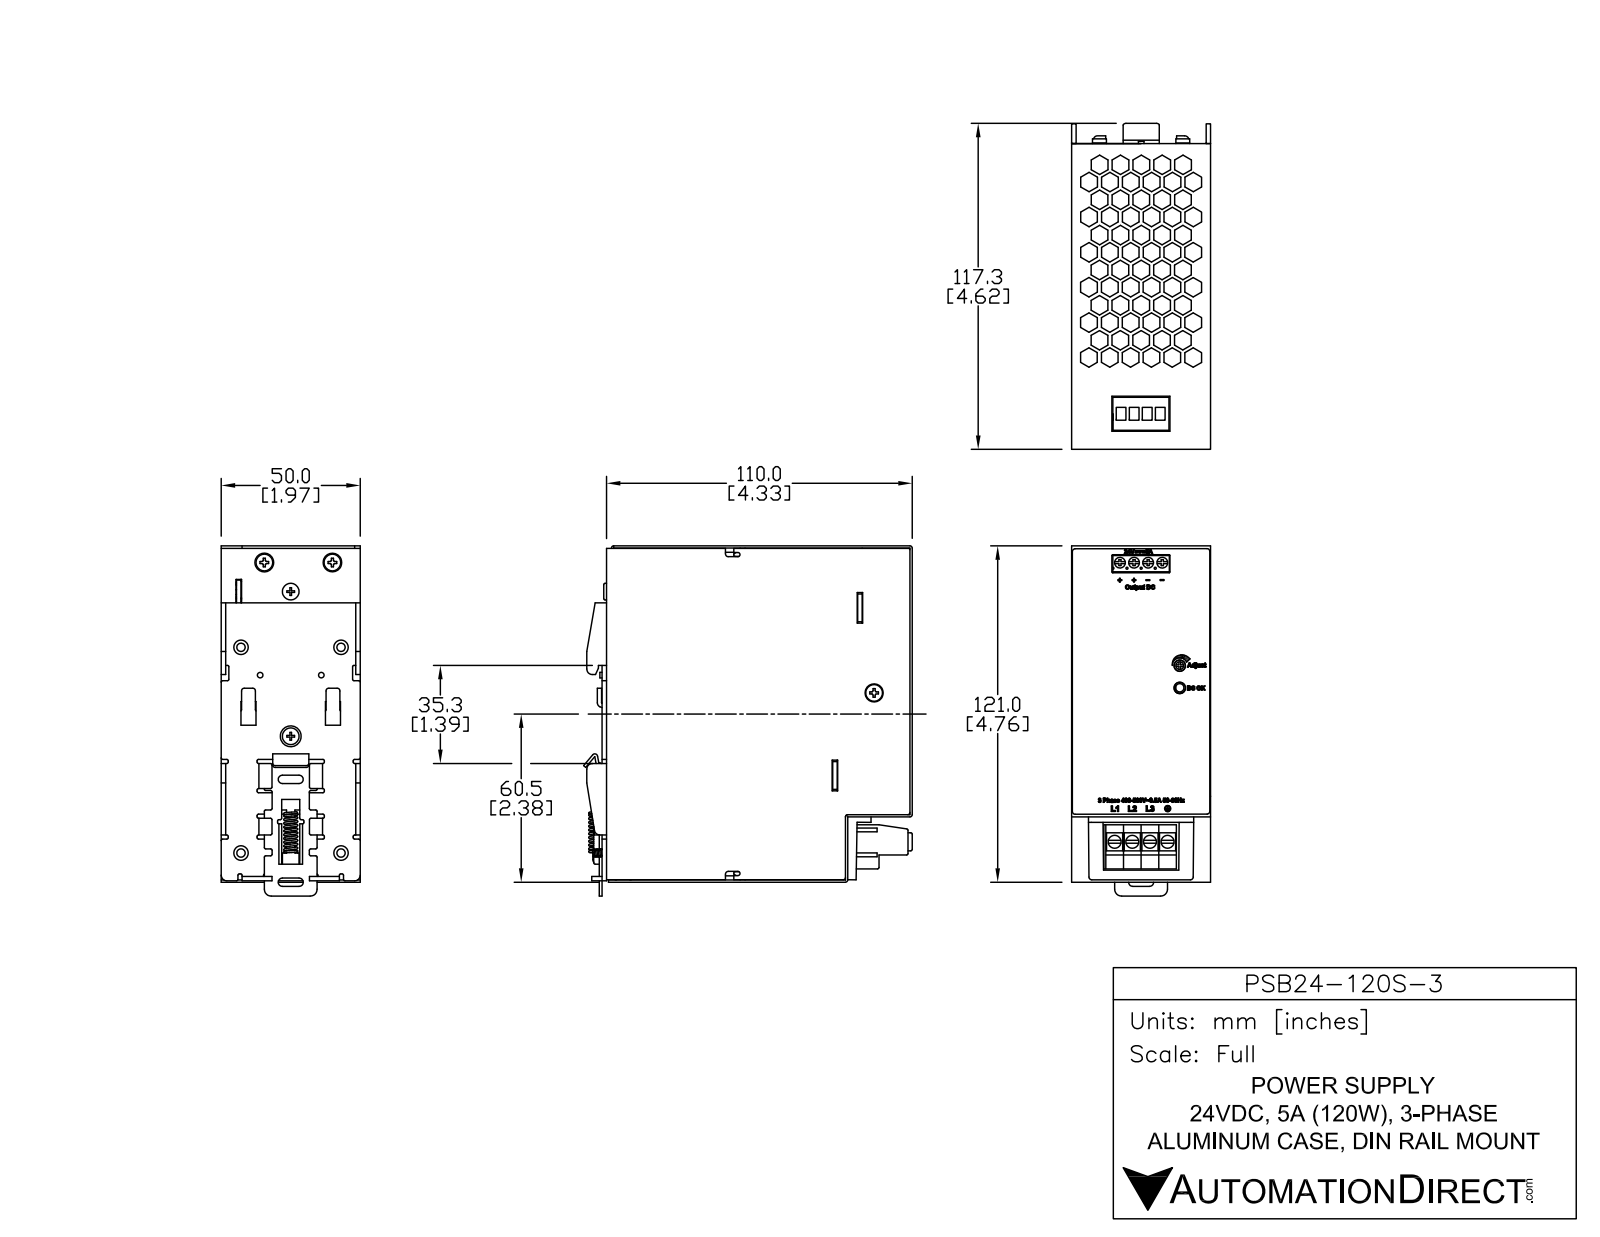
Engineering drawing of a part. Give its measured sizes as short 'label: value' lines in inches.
name: 3105319100; 3103300600; 3462026200_2; ASSY_DCT-1503_ASM (+8 more)
written by: SolidWorks 2014 (AUTOMOTIVE_DESIGN)
unit: in
bodies: 49 solids, 6266 faces (3875 planar, 980 cylindrical, 1411 other)
size: 4.961 × 4.662 × 1.972
volume: 8.063 in³; area: 330.7 in²
holes: 19× ⌀0.098, 9× ⌀0.165, 6× ⌀0.079, 4× ⌀0.071, 4× ⌀0.152, 4× ⌀0.157, 4× ⌀0.159, 4× ⌀0.183, 4× ⌀0.191, 3× ⌀0.161, 2× ⌀0.063, 2× ⌀0.138
bosses: 12× ⌀0.236, 12× ⌀0.118, 6× ⌀0.138, 4× ⌀0.205, 4× ⌀0.187, 4× ⌀0.177, 4× ⌀0.156, 2× ⌀0.197
rounds: 138× R0.02, 54× R0.03, 45× R0.039, 37× R0.004, 32× R0.006, 26× R0.035, 22× R0.035, 14× R0.031
face distances: 0.059, 1.909, 0.063, 0.017, 1.969, 0.076, 1.85, 1.689, 1.833, 1.893
hole spacings: 1.181, 0.2, 0.25, 2.38, 2.461, 2.53, 2.583, 2.658
